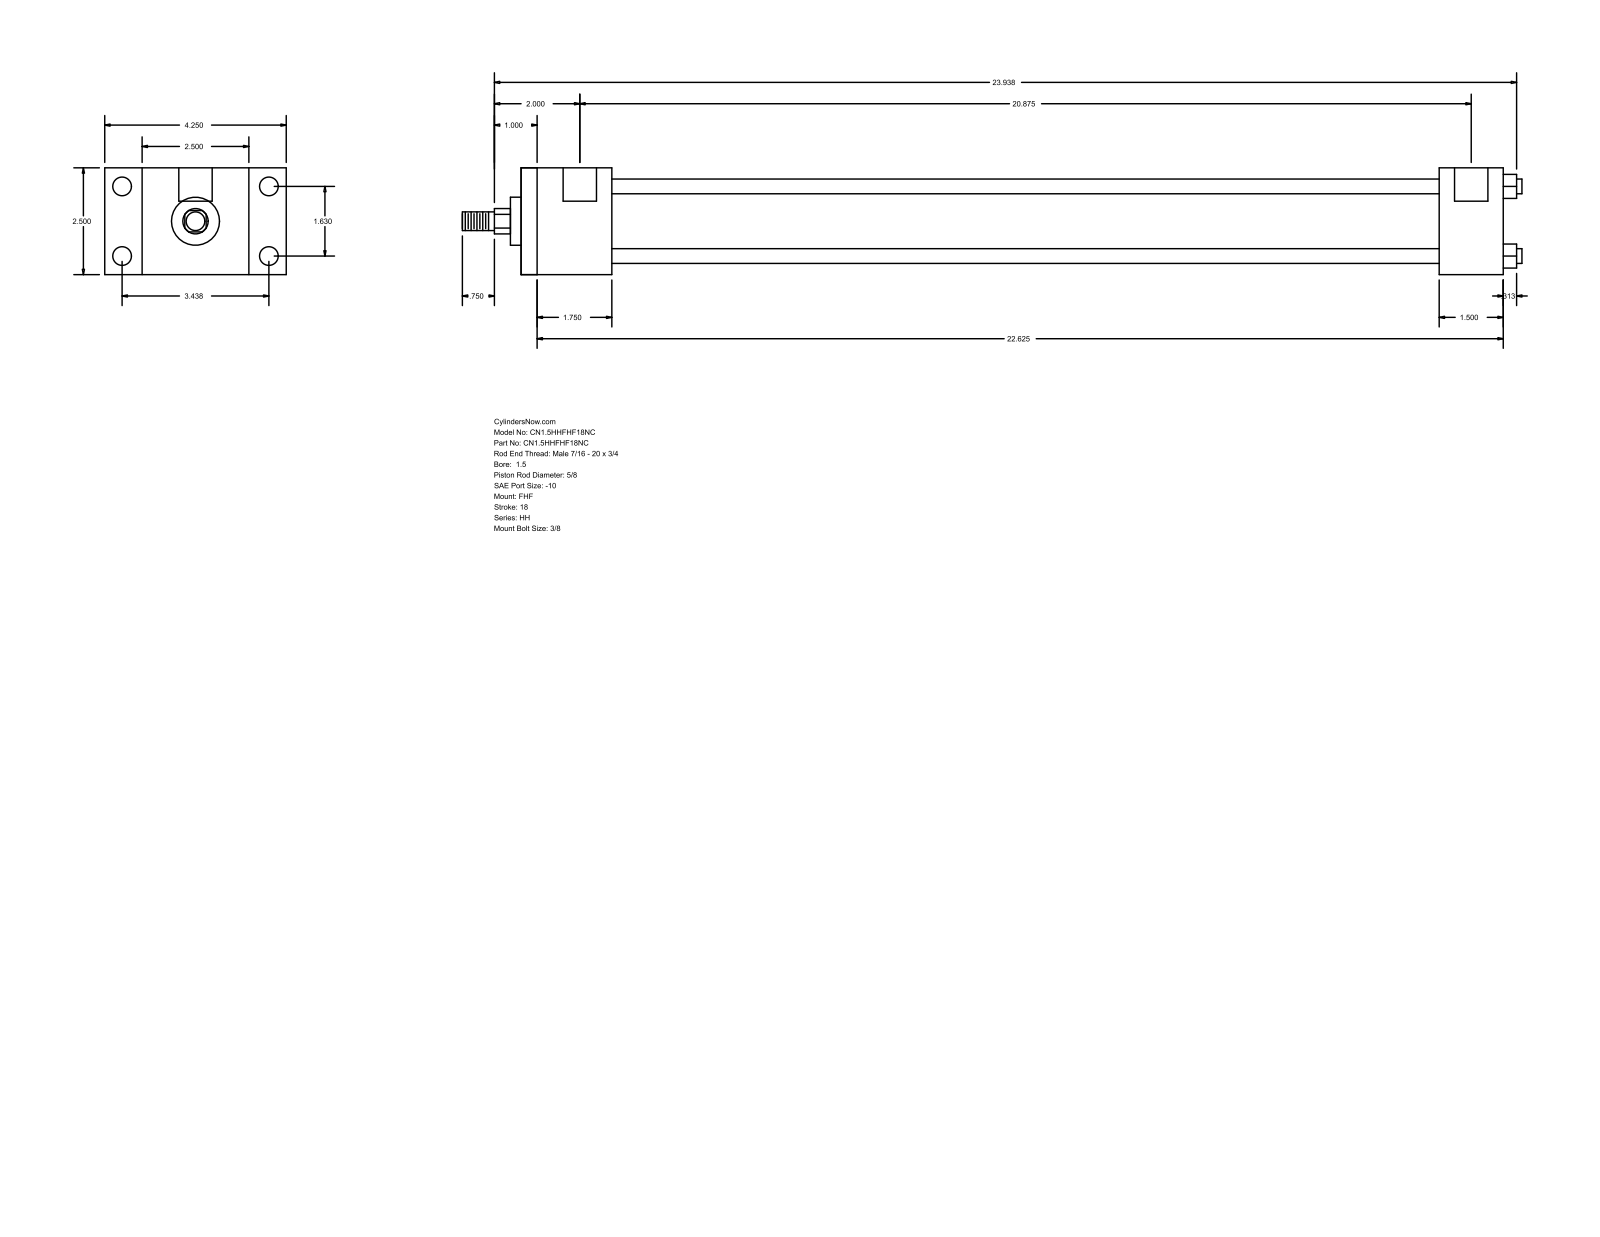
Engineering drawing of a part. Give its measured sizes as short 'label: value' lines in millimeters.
name: HH_FHF__0150_0.625
written by: GSSL Pune (CONFIG_CONTROL_DESIGN)
unit: mm
bodies: 0 solids, 88 faces (60 planar, 28 cylindrical, 0 other)
size: 630.24 × 107.95 × 63.5
holes: 4× ⌀5.56, 4× ⌀11.13, 2× ⌀19.84
bosses: 4× ⌀8.76, 1× ⌀44.45, 1× ⌀28.57, 1× ⌀15.88, 1× ⌀11.11
rounds: 1× R7.54
face distances: 63.5, 22.23, 85.73, 53.97, 107.96, 584.2, 530.23, 38.1, 546.1, 492.13
hole spacings: 1.59, 41.4, 87.32, 96.64, 531.81, 533.4, 530.22
